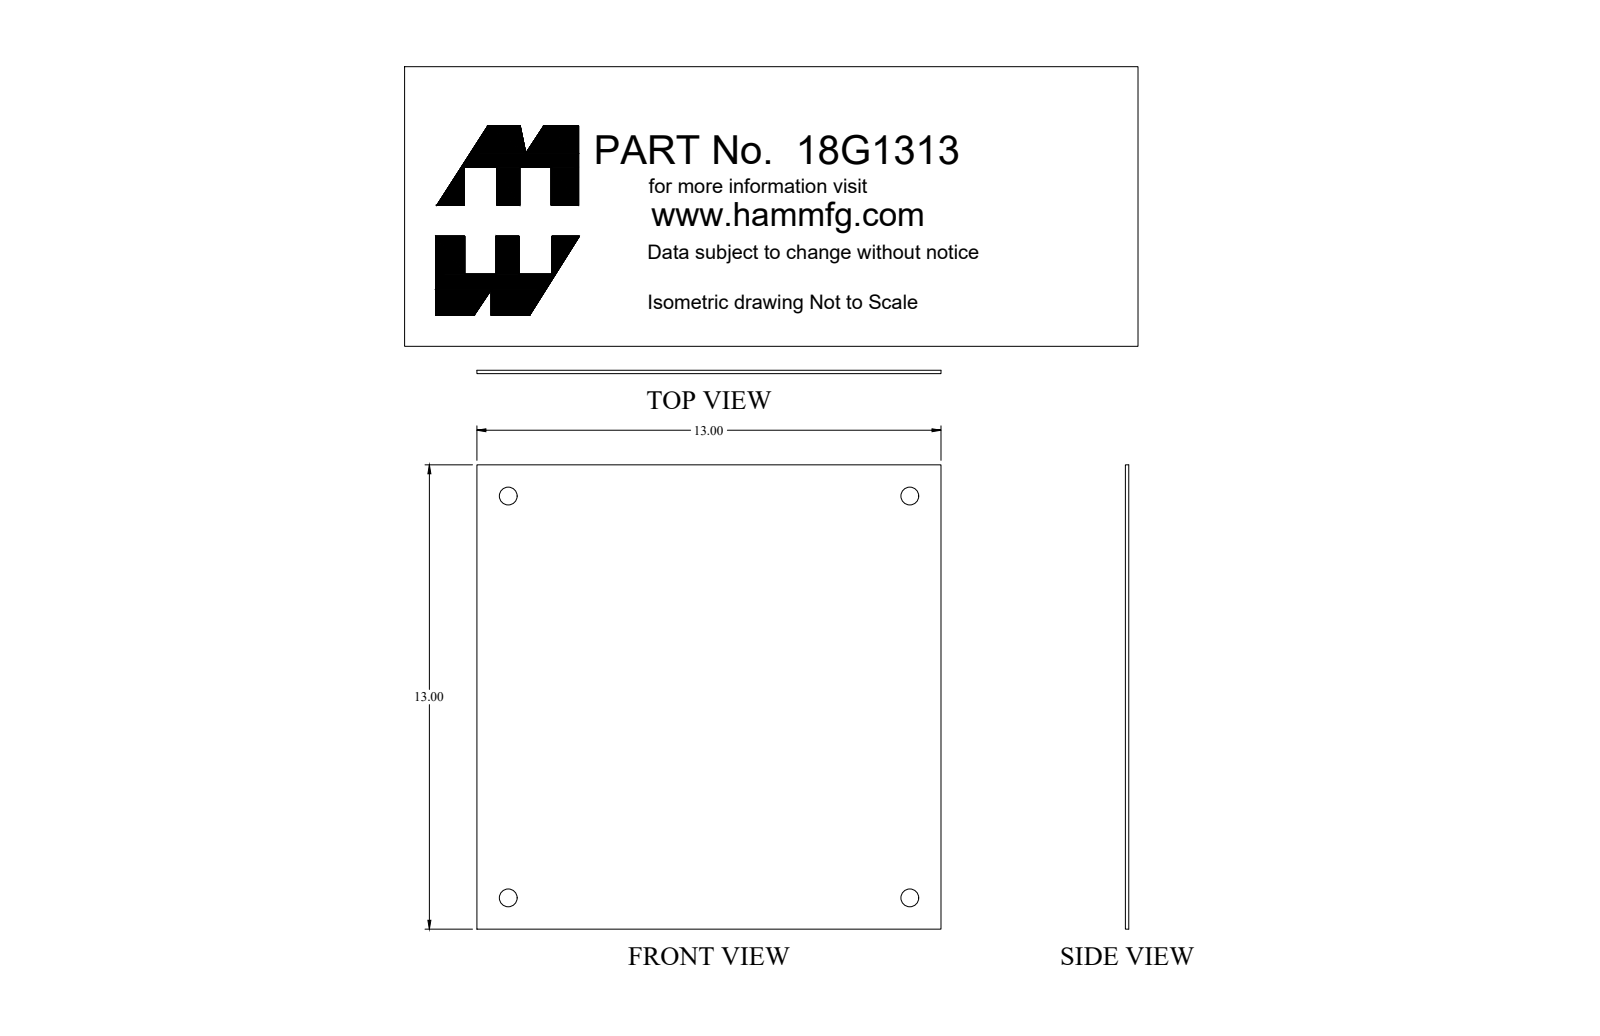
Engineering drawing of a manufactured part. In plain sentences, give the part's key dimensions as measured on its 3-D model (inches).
The part is named "18G1313". Its 3-D file was written by "SolidWorks 2018 (AUTOMOTIVE_DESIGN)". It is 1 solid with 10 faces: 6 planar, 4 cylindrical and 0 other. Overall it measures 13 by 13 by 0.095 inches. Its volume is 15.98 cubic inches and its surface area 342 square inches. Round holes: 4 of diameter 0.5. The main face-to-face distances are 0.095, 13. The hole center spacings are 11.25, 15.911.
